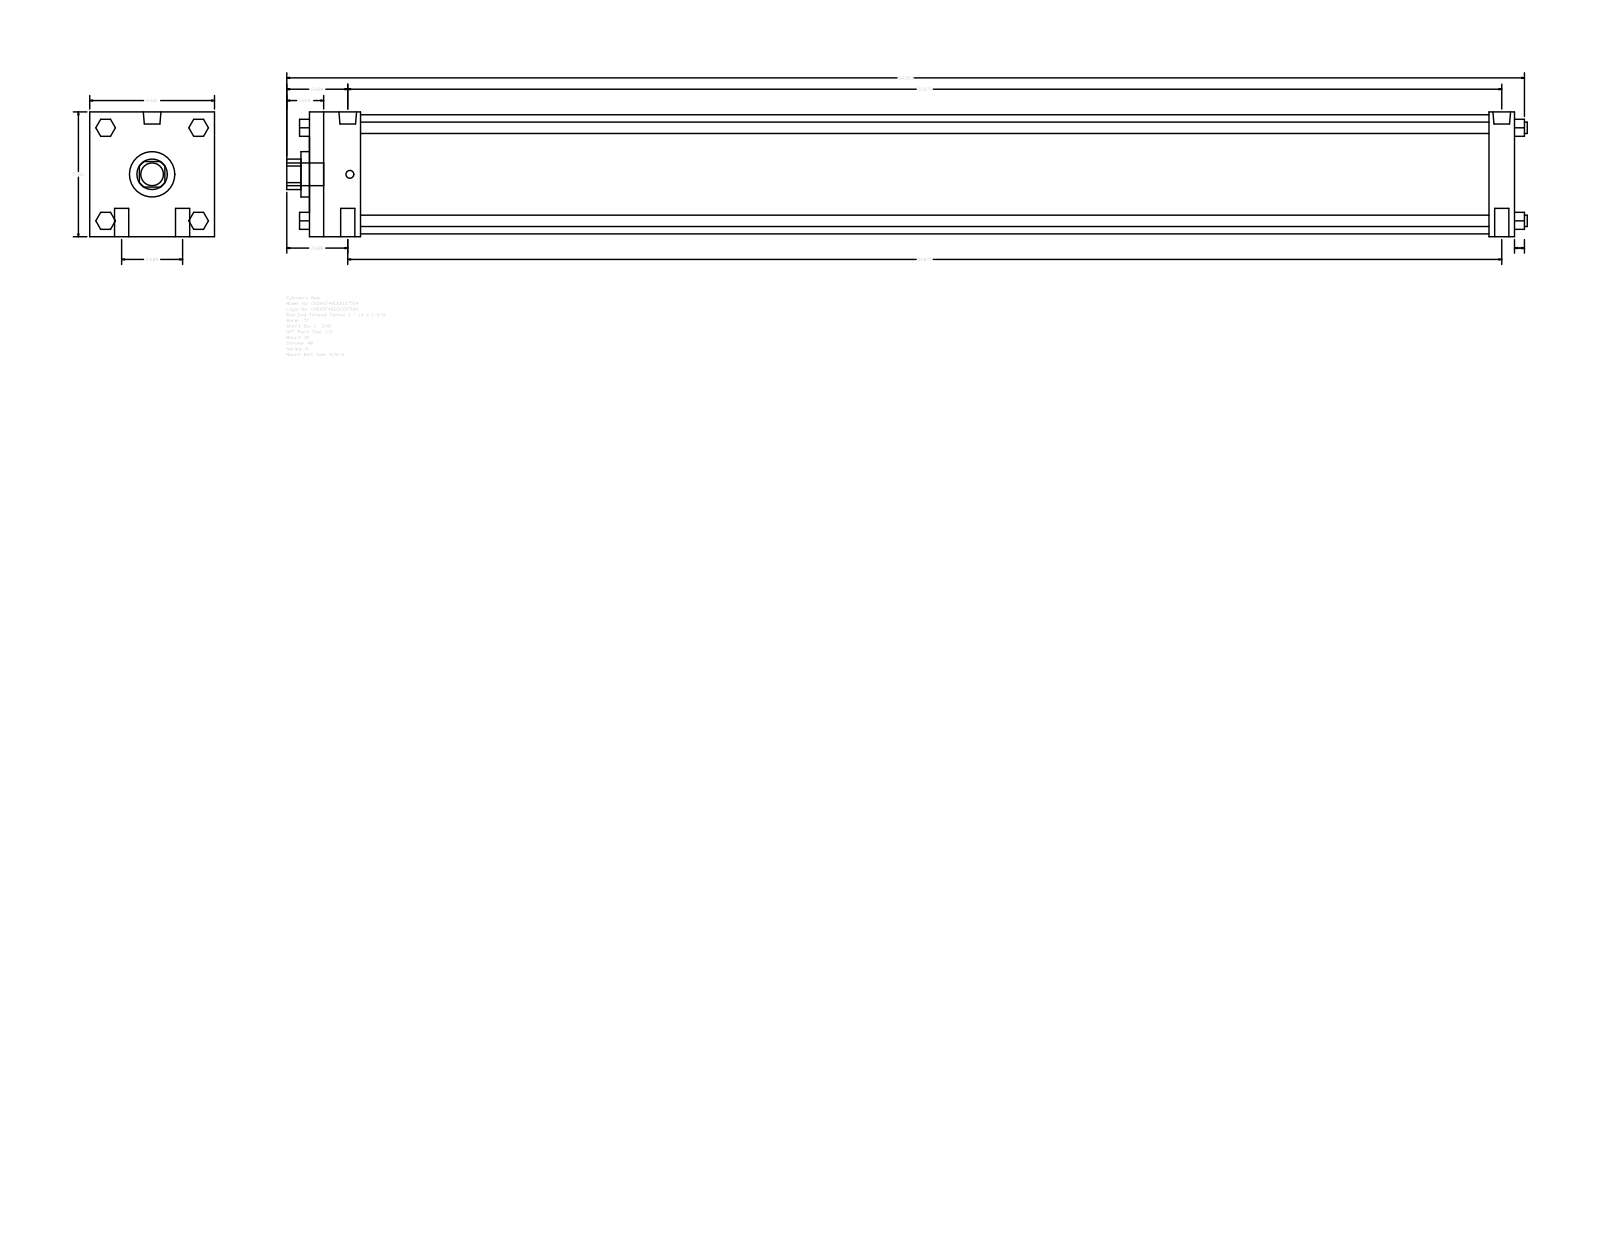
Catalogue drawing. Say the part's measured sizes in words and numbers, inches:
The part is named "A_SF__0500_1.375". Its 3-D file was written by "GSSL Pune (CONFIG_CONTROL_DESIGN)". It is 0 solids with 124 faces: 94 planar, 30 cylindrical and 0 other. Overall it measures 54.687 by 5.5 by 5.5 inches. Round holes: 1 of diameter 1.375, 1 of diameter 2, 1 of diameter 5.25. Round bosses or shafts: 4 of diameter 0.625, 4 of diameter 0.5, 2 of diameter 0.778, 2 of diameter 0.344, 1 of diameter 1. Partial cylindrical surfaces (rounded edges, fillets, slot ends): 1 of radius 0.672. The main face-to-face distances are 5.5, 53.125, 1.125, 2.25, 52, 49.75, 50.875, 0.75, 2.05, 3.55.
